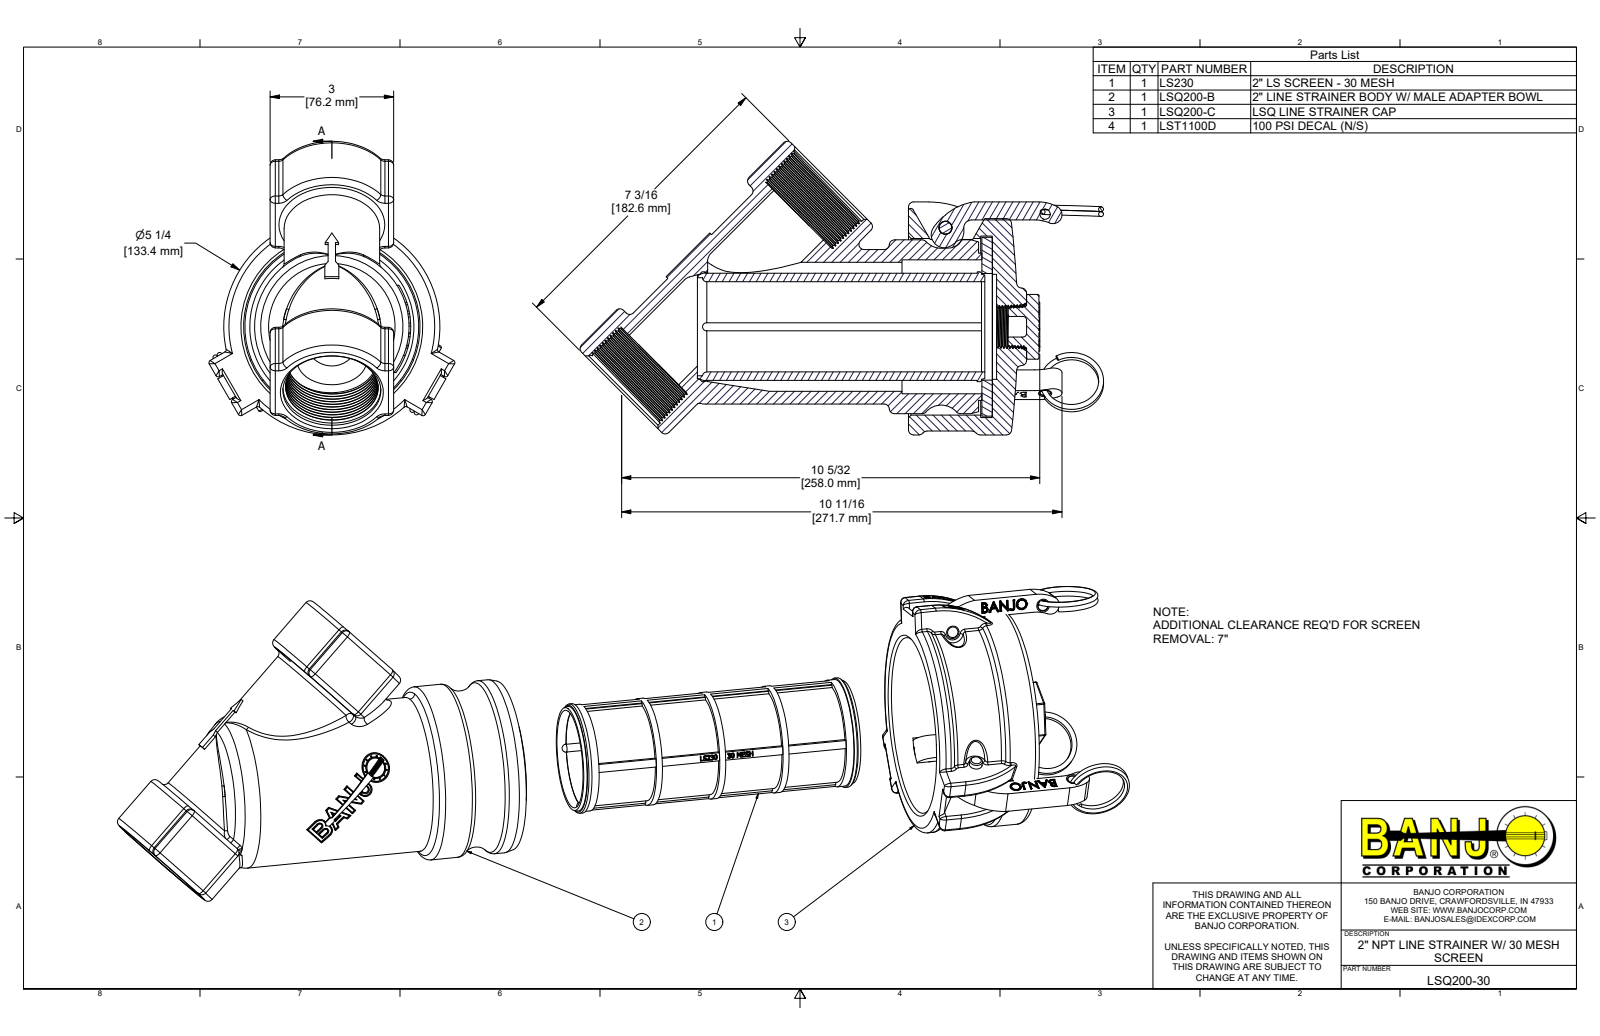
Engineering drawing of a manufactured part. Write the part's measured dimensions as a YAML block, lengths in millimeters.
part_name: "LSQ200-30; LSQ200-B; LSQ200-C; LSQ200-MYC (+8 more)"
step_written_by: "Autodesk Inventor 2019 (AUTOMOTIVE_DESIGN)"
units: millimeters
bodies: {solids: 15, faces: 3462, planar: 1192, cylindrical: 828, other: 1442}
overall_size: [484.2, 181, 151.7]
volume: 1236000
surface_area: 410400
round_holes:
  - {diameter: 6.4, count: 3}
  - {diameter: 7.9, count: 3}
  - {diameter: 8.1, count: 3}
  - {diameter: 43.2, count: 2}
  - {diameter: 11.5, count: 1}
  - {diameter: 12.7, count: 1}
  - {diameter: 16.3, count: 1}
  - {diameter: 55.6, count: 1}
  - {diameter: 59.7, count: 1}
  - {diameter: 64.8, count: 1}
  - {diameter: 65.8, count: 1}
  - {diameter: 79.5, count: 1}
round_bosses_or_shafts:
  - {diameter: 8.3, count: 3}
  - {diameter: 7.9, count: 3}
  - {diameter: 133.4, count: 1}
  - {diameter: 110.2, count: 1}
  - {diameter: 107.2, count: 1}
  - {diameter: 95.3, count: 1}
  - {diameter: 90.7, count: 1}
  - {diameter: 67.7, count: 1}
partial_cylinders:
  - {radius: 0.2, count: 353}
  - {radius: 0.1, count: 51}
  - {radius: 3.2, count: 47}
  - {radius: 1.5, count: 27}
  - {radius: 0.8, count: 18}
  - {radius: 23.6, count: 6}
  - {radius: 6.4, count: 5}
  - {radius: 2.5, count: 4}
face_to_face_distances: [6.4, 6.5, 51.8, 51.7, 45.3, 11.4, 15.5, 2.5, 9, 0.8]
hole_center_spacings: [62, 85.3, 144.4]
